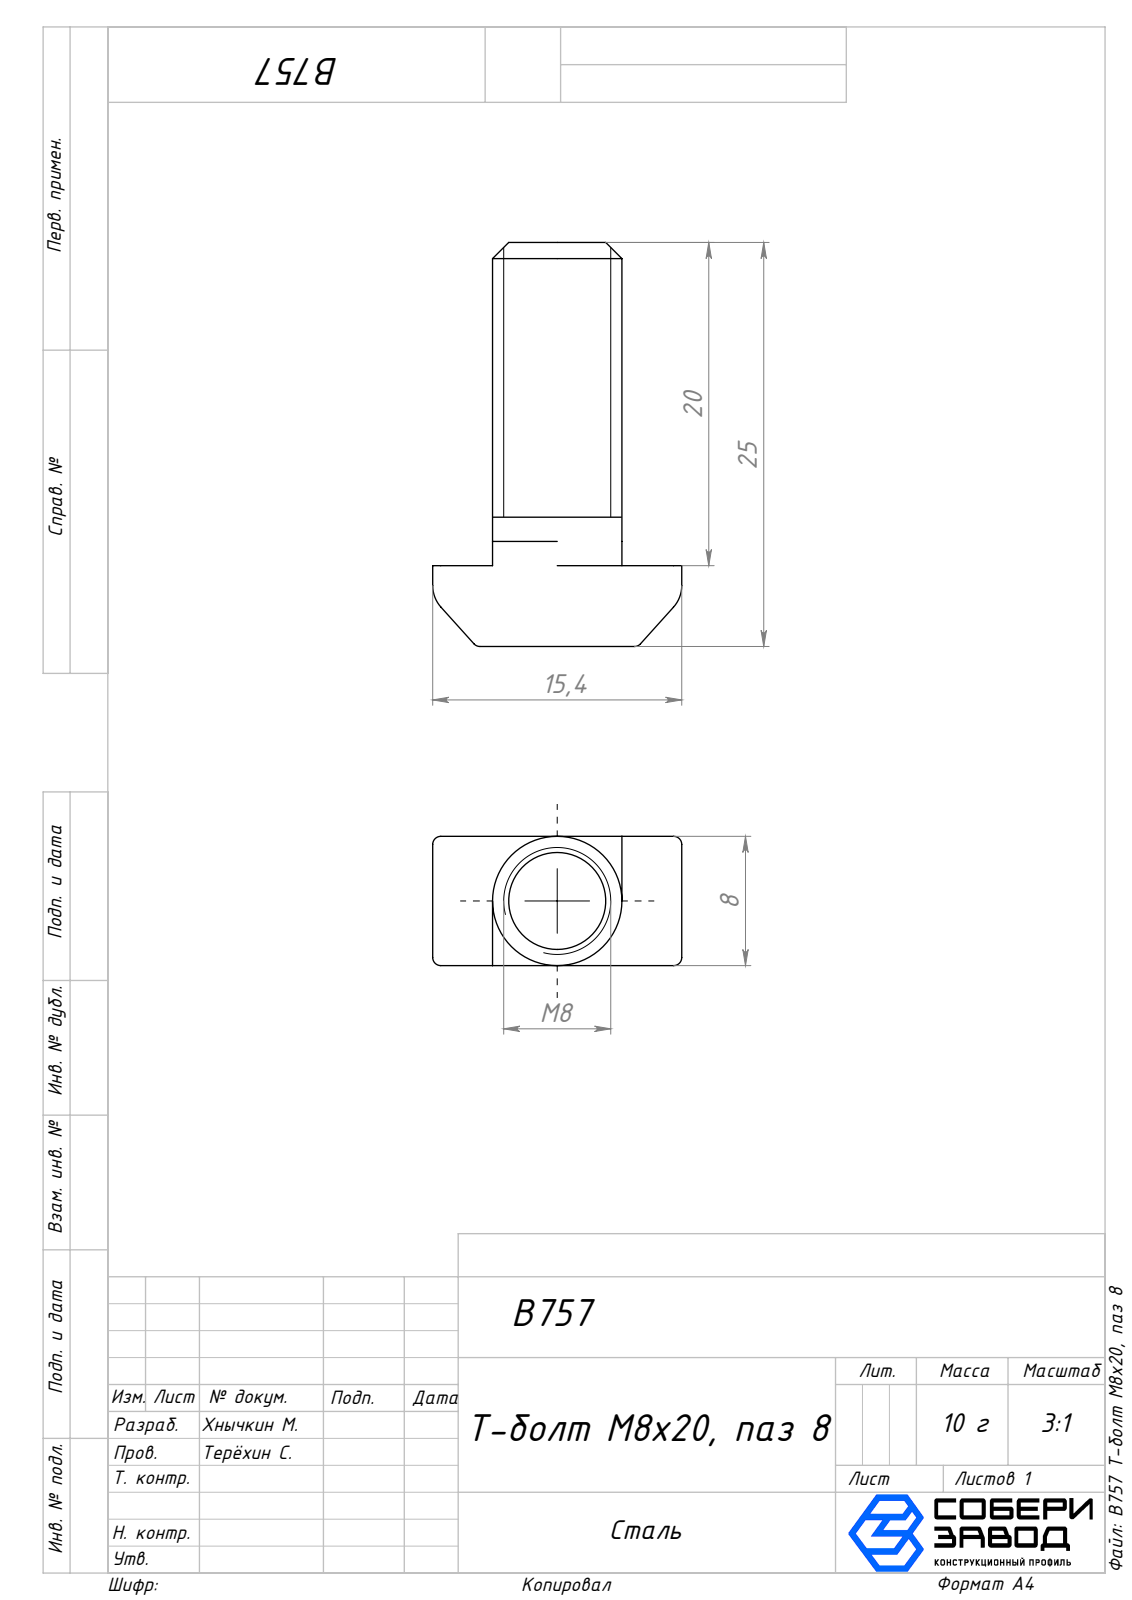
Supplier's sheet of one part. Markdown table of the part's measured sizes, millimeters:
| quantity | value |
| --- | --- |
| part name | B757 Т-болт М8х20, паз 8 |
| STEP written by | SolidWorks 2025 (AUTOMOTIVE_DESIGN) |
| units | millimeters |
| bodies | 1 solid, 40 faces (14 planar, 16 cylindrical, 10 other) |
| overall size | 25 × 15.4 × 8 |
| volume | 1 552 mm³ |
| surface area | 918 mm² |
| round bosses / shafts (diameter × count) | 8 × 1 |
| partial cylindrical surfaces (radius × count) | 0.5 × 12, 2 × 2 |
| main face-to-face distances | 8, 5, 25, 20, 3.7, 11.7, 15.4, 6.5, 1.5, 18.5 |
